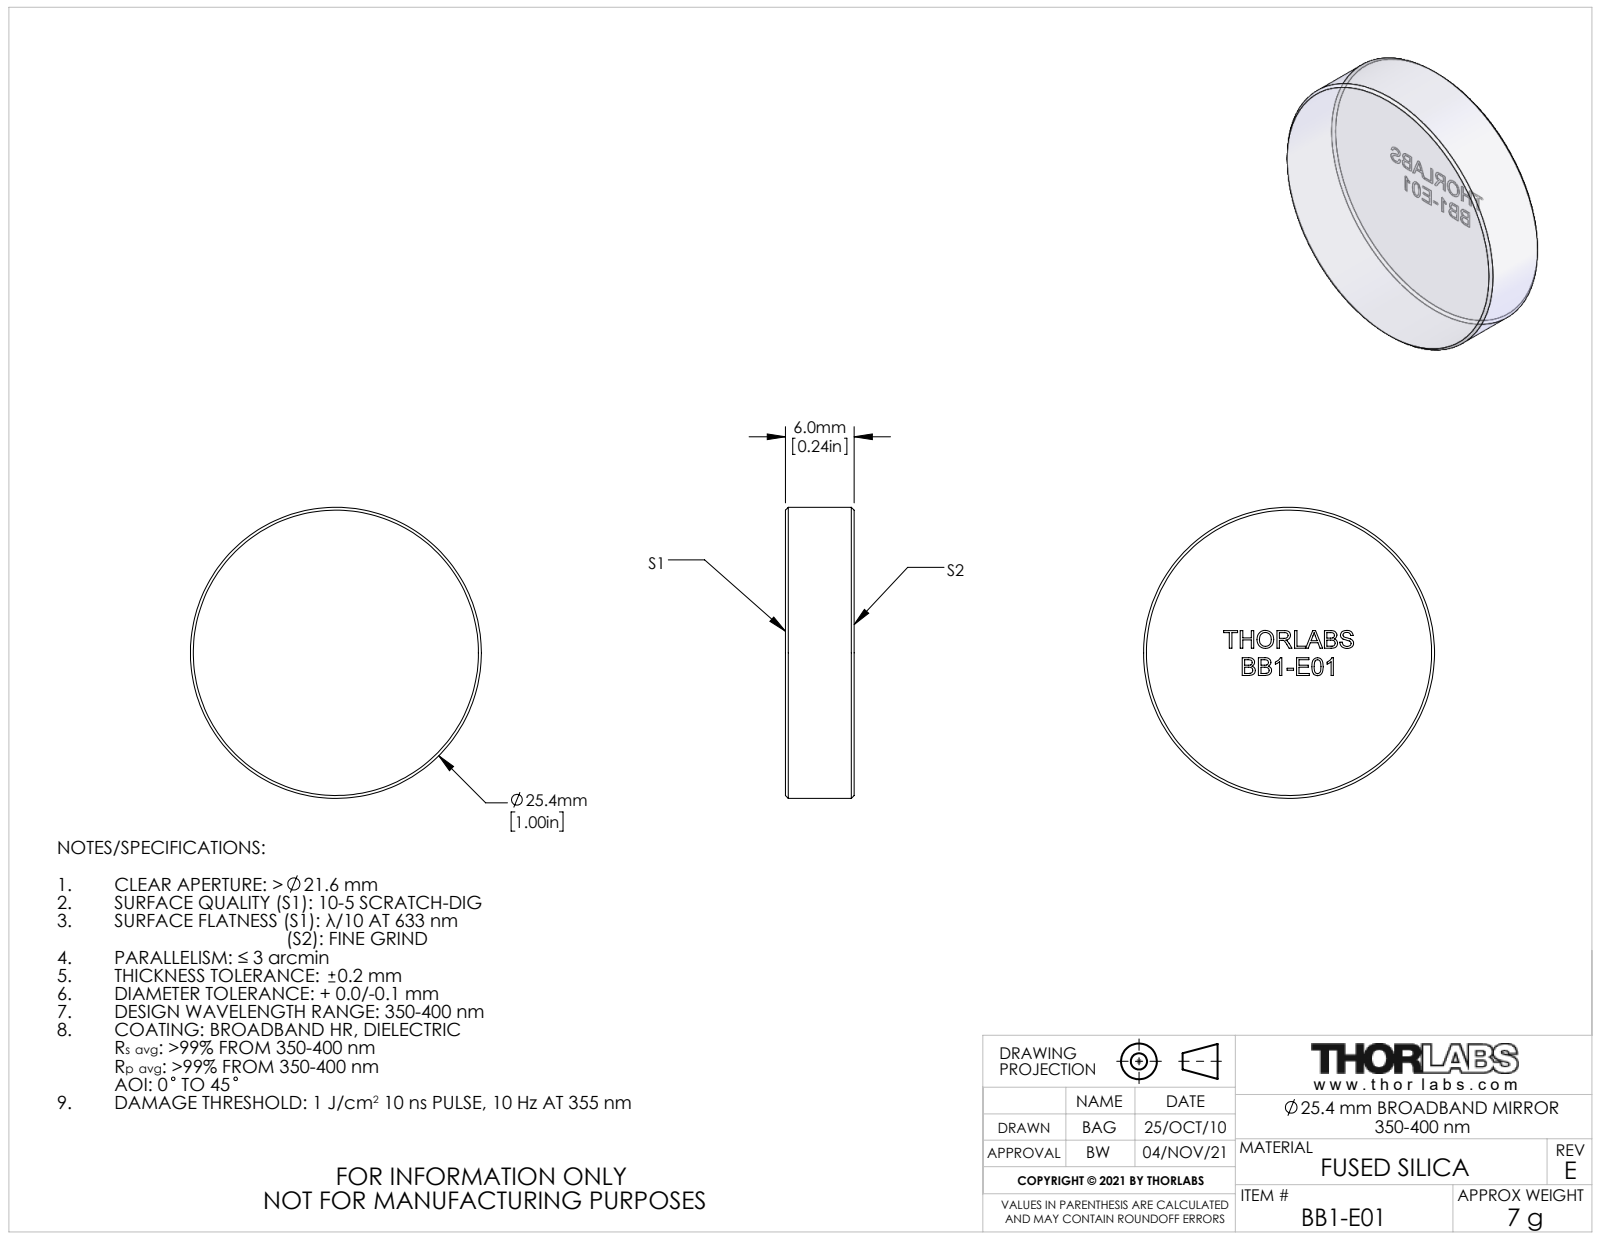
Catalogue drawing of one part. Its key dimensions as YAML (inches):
part_name: "3538-E0W"
step_written_by: "SolidWorks 2016 (CONFIG_CONTROL_DESIGN)"
units: inches
bodies: {solids: 1, faces: 212, planar: 130, cylindrical: 2, other: 80}
overall_size: [1, 1, 0.236]
volume: 0.185
surface_area: 2.277
round_bosses_or_shafts:
  - {diameter: 1, count: 1}
face_to_face_distances: [0.236, 0.061, 0.093, 0.147, 0.054, 0.163, 0.119, 0.187, 0.033, 0.126]
